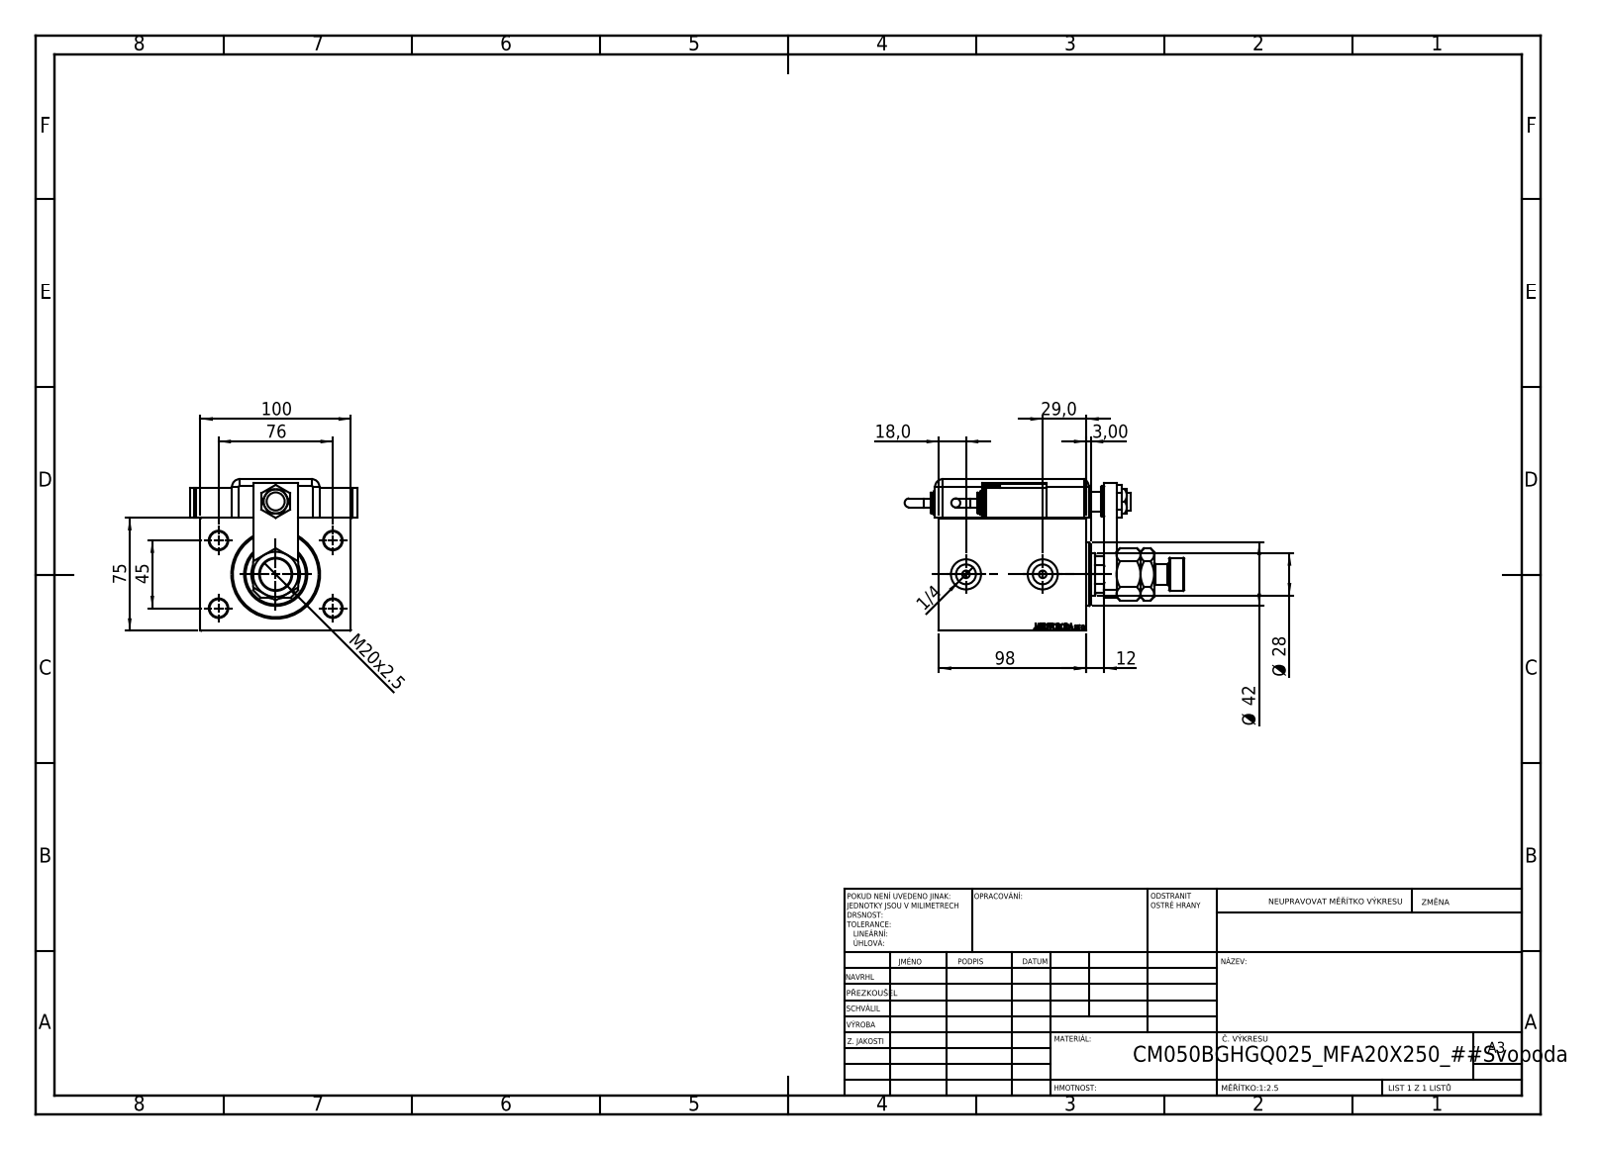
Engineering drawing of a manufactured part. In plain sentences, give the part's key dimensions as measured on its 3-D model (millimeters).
The part is named "SWITCH_Q_FRONT_BACK; MAGNETIC SWITCH Q; KRYT; V450CM_B_Body (+7 more)". Its 3-D file was written by "SolidWorks 2019 (CONFIG_CONTROL_DESIGN)". It is 14 solids with 1320 faces: 624 planar, 115 cylindrical and 581 other. Overall it measures 185.76 by 111 by 100.8 millimeters. Its volume is 845 699 cubic millimeters and its surface area 154 503 square millimeters. Round holes: 5 of diameter 12, 3 of diameter 20, 2 of diameter 4, 2 of diameter 5, 2 of diameter 8, 2 of diameter 13.16, 1 of diameter 13, 1 of diameter 14, 1 of diameter 18.5, 1 of diameter 28, 1 of diameter 31.5, 1 of diameter 32.5. Round bosses or shafts: 3 of diameter 20, 3 of diameter 14, 2 of diameter 16, 2 of diameter 6, 1 of diameter 42, 1 of diameter 22. Partial cylindrical surfaces (rounded edges, fillets, slot ends): 9 of radius 5, 1 of radius 10, 1 of radius 13.5. The main face-to-face distances are 75, 3, 98, 100, 14, 20, 84, 25.8, 100.8, 13.5. The hole center spacings are 44.16, 45, 46.04, 76, 80.53, 88.32, 20, 48.5.
